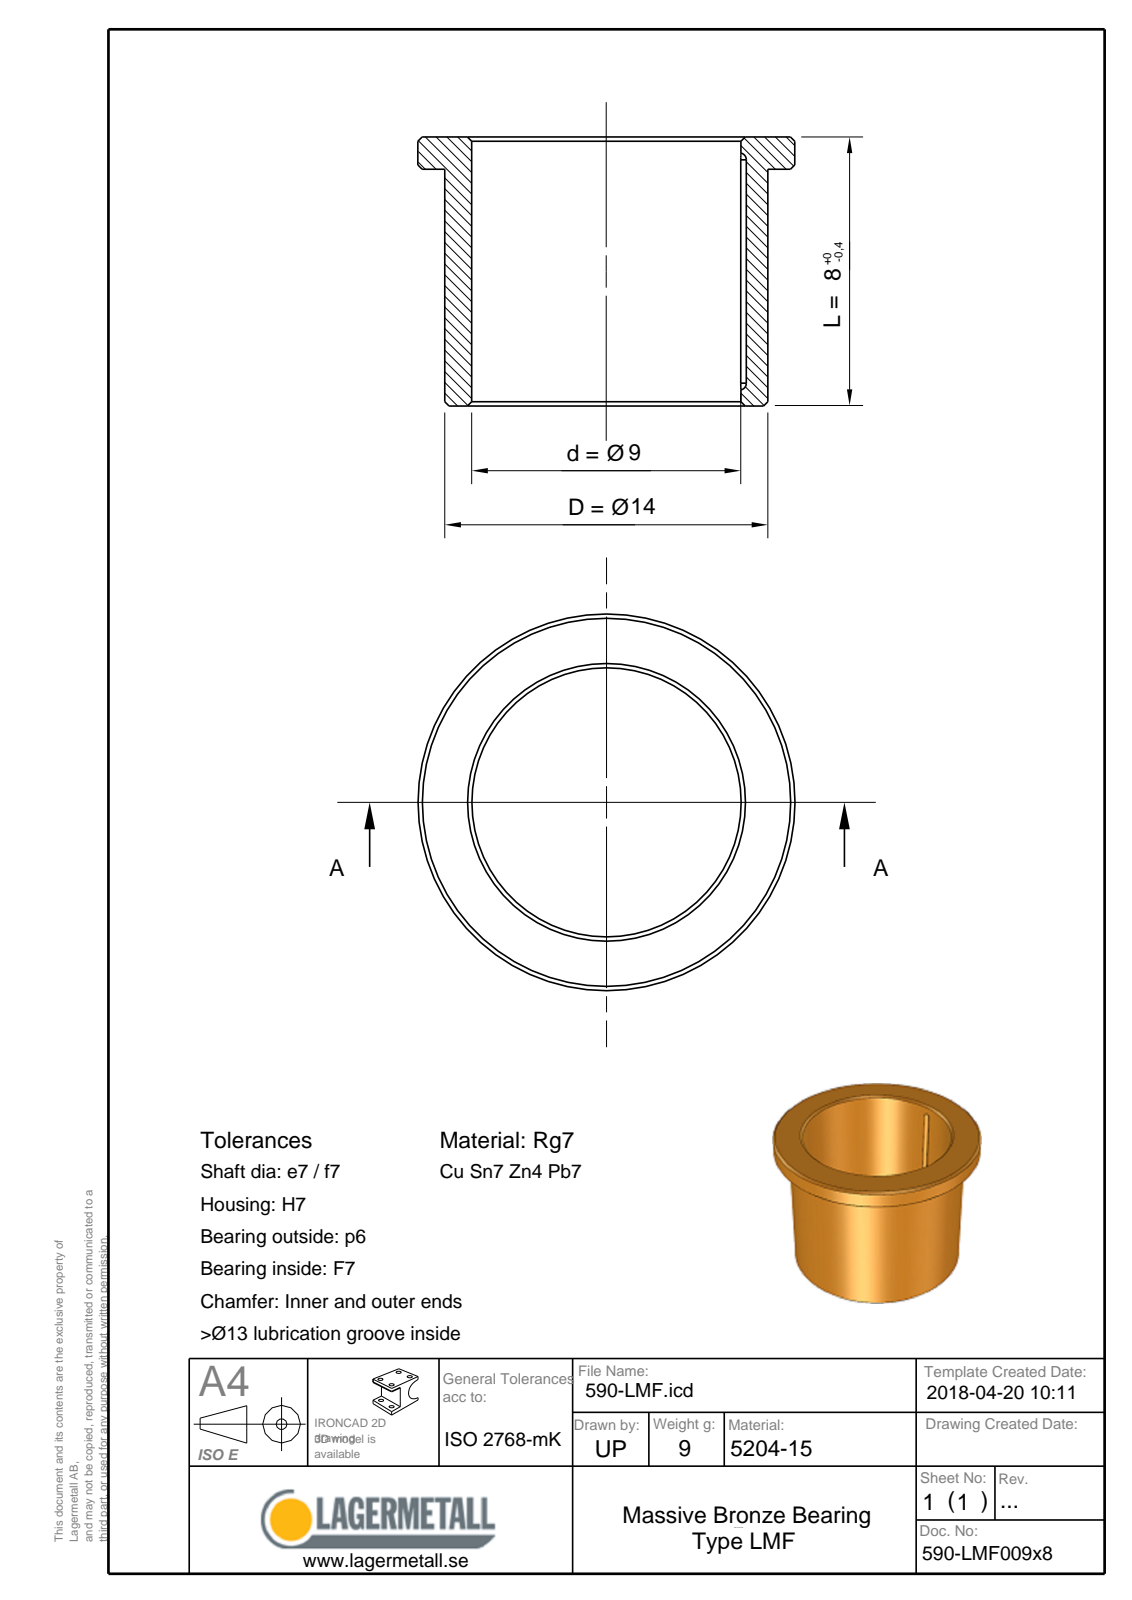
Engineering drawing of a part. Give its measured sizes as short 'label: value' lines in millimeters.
name: 590-LMF009x8
written by: Spatial InterOp 3D (CONFIG_CONTROL_DESIGN)
unit: mm
bodies: 1 solid, 11 faces (3 planar, 3 cylindrical, 5 other)
size: 18 × 18 × 8
volume: 1 015 mm³; area: 960 mm²
holes: 1× ⌀9
bosses: 1× ⌀18, 1× ⌀14
face distances: 3, 5, 8
